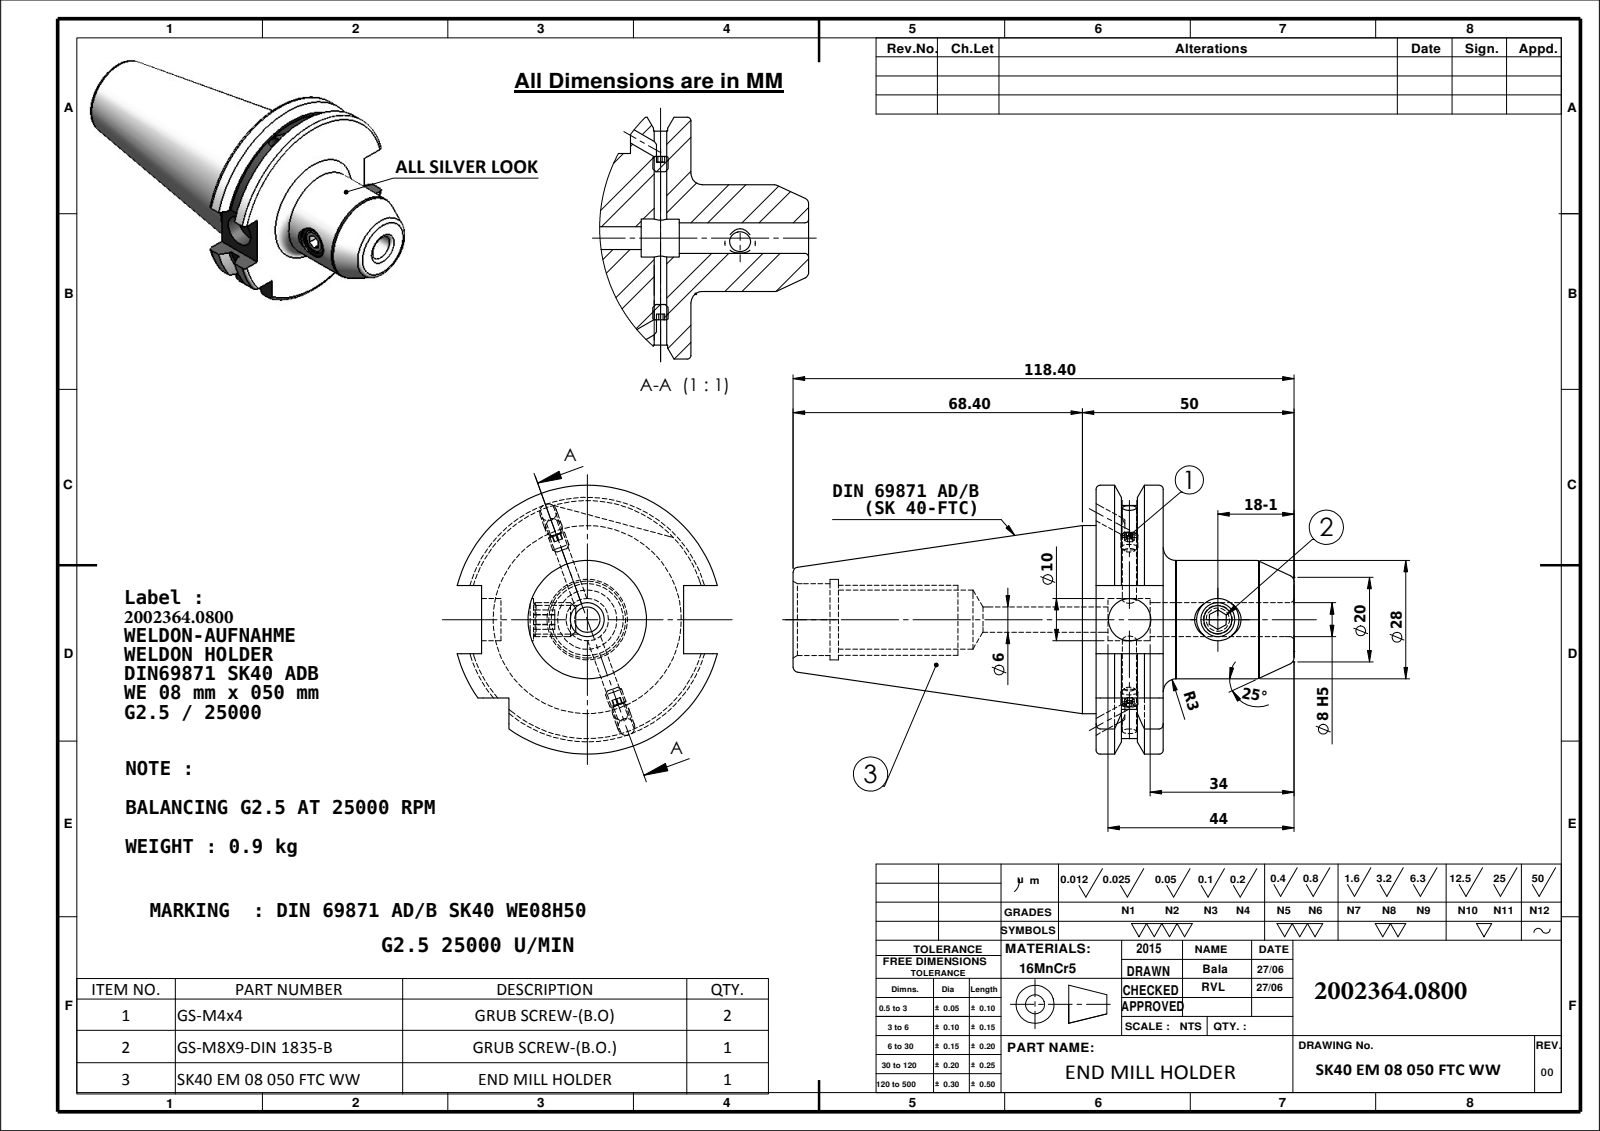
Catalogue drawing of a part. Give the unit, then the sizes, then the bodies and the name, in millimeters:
Units: millimetres
Overall size (bounding box): 118.4 × 63.55 × 61.48
Round holes (diameter × count): ⌀10 ×3, ⌀3.3 ×1, ⌀6 ×1, ⌀6.8 ×1, ⌀8 ×1, ⌀14 ×1, ⌀17 ×1, ⌀19 ×1
Round bosses / shafts (diameter × count): ⌀4 ×2, ⌀44.45 ×1, ⌀28 ×1, ⌀8 ×1
Partial cylindrical surfaces — rounded edges, fillets, slot ends (radius × count): R28.12 ×1, R31.77 ×1
Main face-to-face distances: 15.9, 46.8, 30.9, 16.1, 47.8, 71.6, 87.5, 118.4, 10.7, 60.9
Hole centre spacings: 20.85
Volume: 119 566 mm³ · Surface area: 24 311 mm²
Bodies: 4 solids, 156 faces (58 planar, 44 cylindrical, 54 other)
Part name (STEP PRODUCT): Copy of M4X4_DIN 913 - M4 x 4-N; M8X10._DIN 913 - M8 x 8-N; 91406-WE7 08050; SK40 EM 08 050 FTC WW
STEP written by: SolidWorks 2009 (CONFIG_CONTROL_DESIGN)
